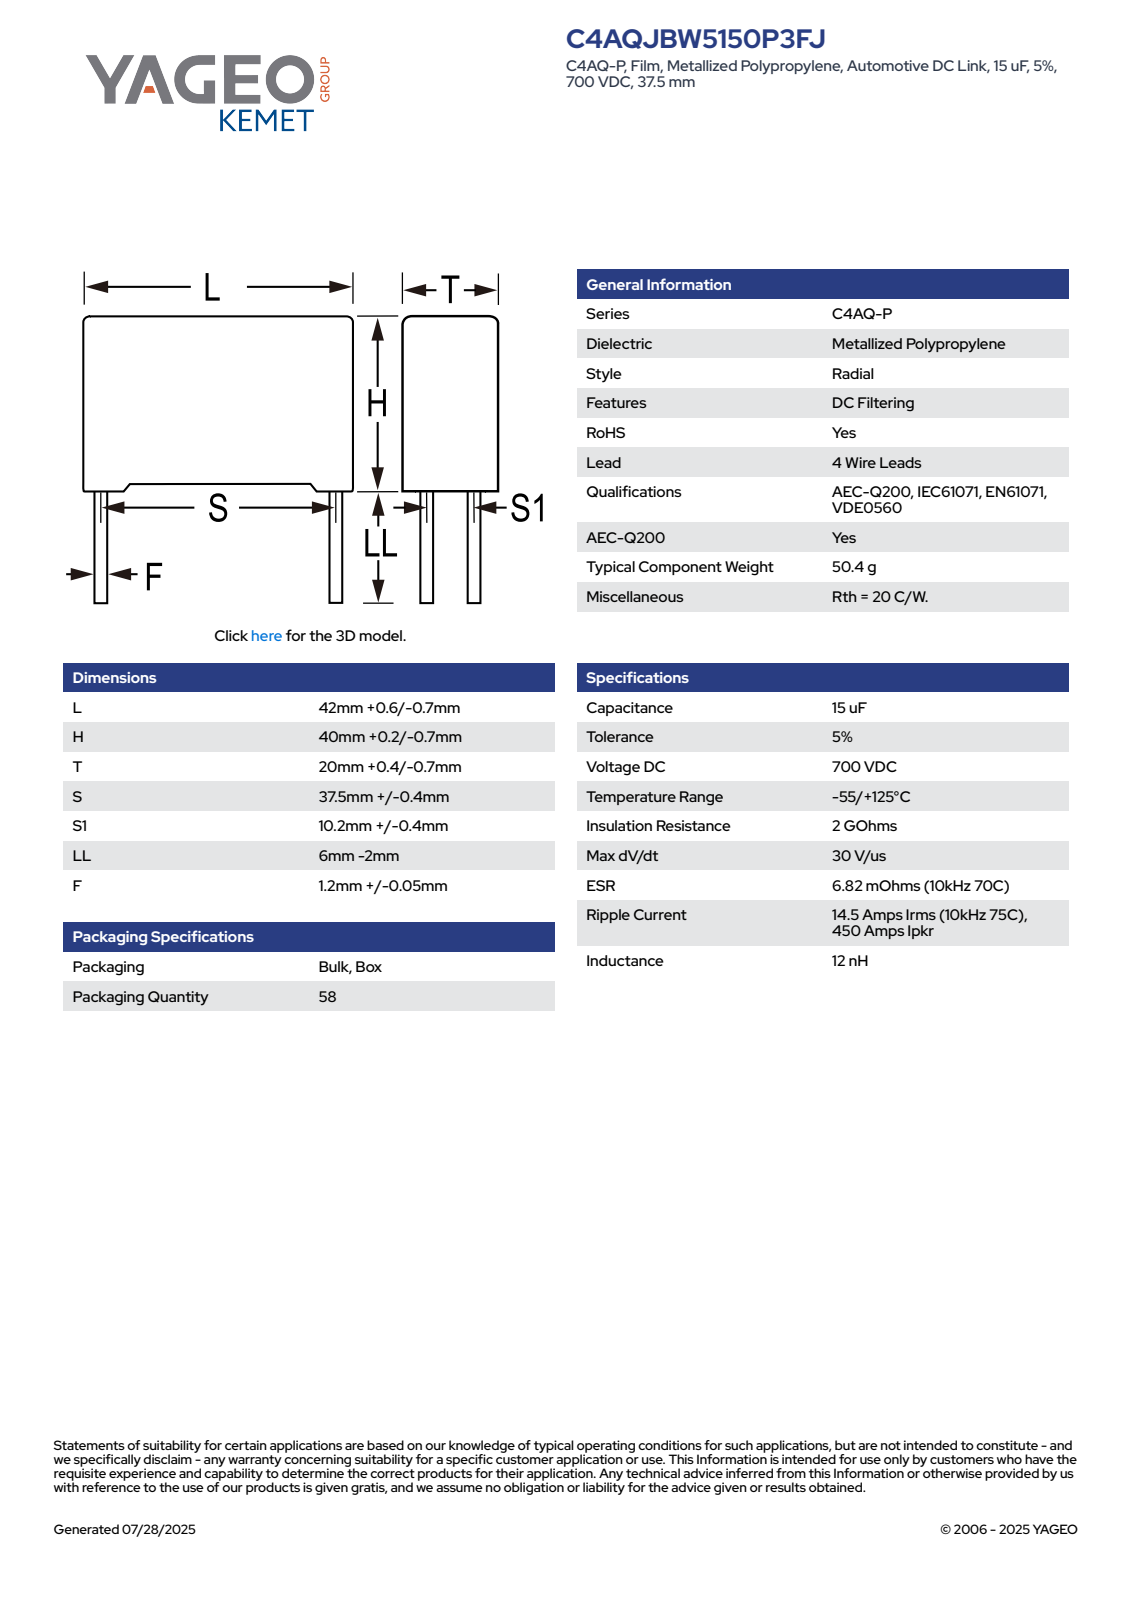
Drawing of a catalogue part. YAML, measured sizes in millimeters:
part_name: "CFP_RB4_42X40X20_L42.6H40.2T20.4S37.5S110.2LL4F1.25"
step_written_by: "SolidWorks 2014 (AUTOMOTIVE_DESIGN)"
units: millimeters
bodies: {solids: 4, faces: 87, planar: 79, cylindrical: 8, other: 0}
overall_size: [44.2, 42.6, 20.41]
volume: 34031
surface_area: 7011
round_bosses_or_shafts:
  - {diameter: 1.25, count: 4}
face_to_face_distances: [20.4, 42.6, 39.02, 1.18, 40.2, 1.25, 20.41, 41.35, 19.15, 40.1]
